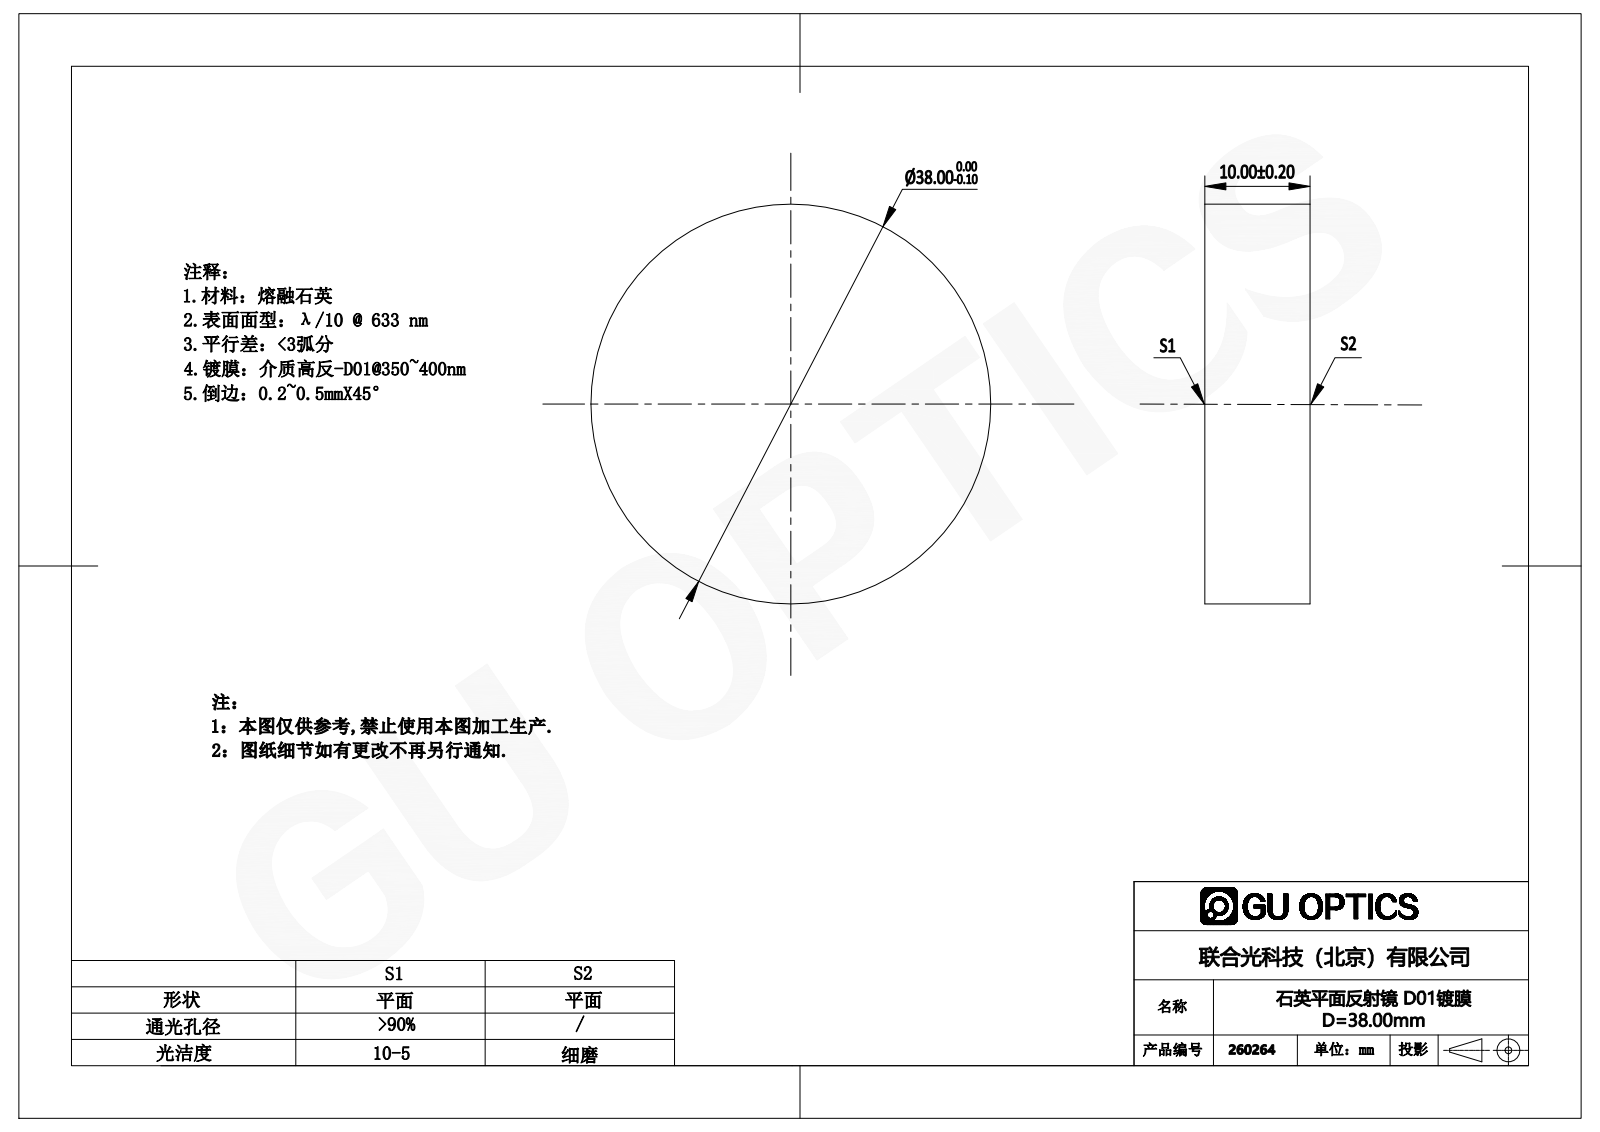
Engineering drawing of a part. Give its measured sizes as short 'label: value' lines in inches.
name: 260075
written by: SolidWorks 2016 (AUTOMOTIVE_DESIGN)
unit: in
bodies: 1 solid, 6 faces (0 planar, 0 cylindrical, 6 other)
size: 1.5 × 1.5 × 0.398
volume: 0.695 in³; area: 5.383 in²
